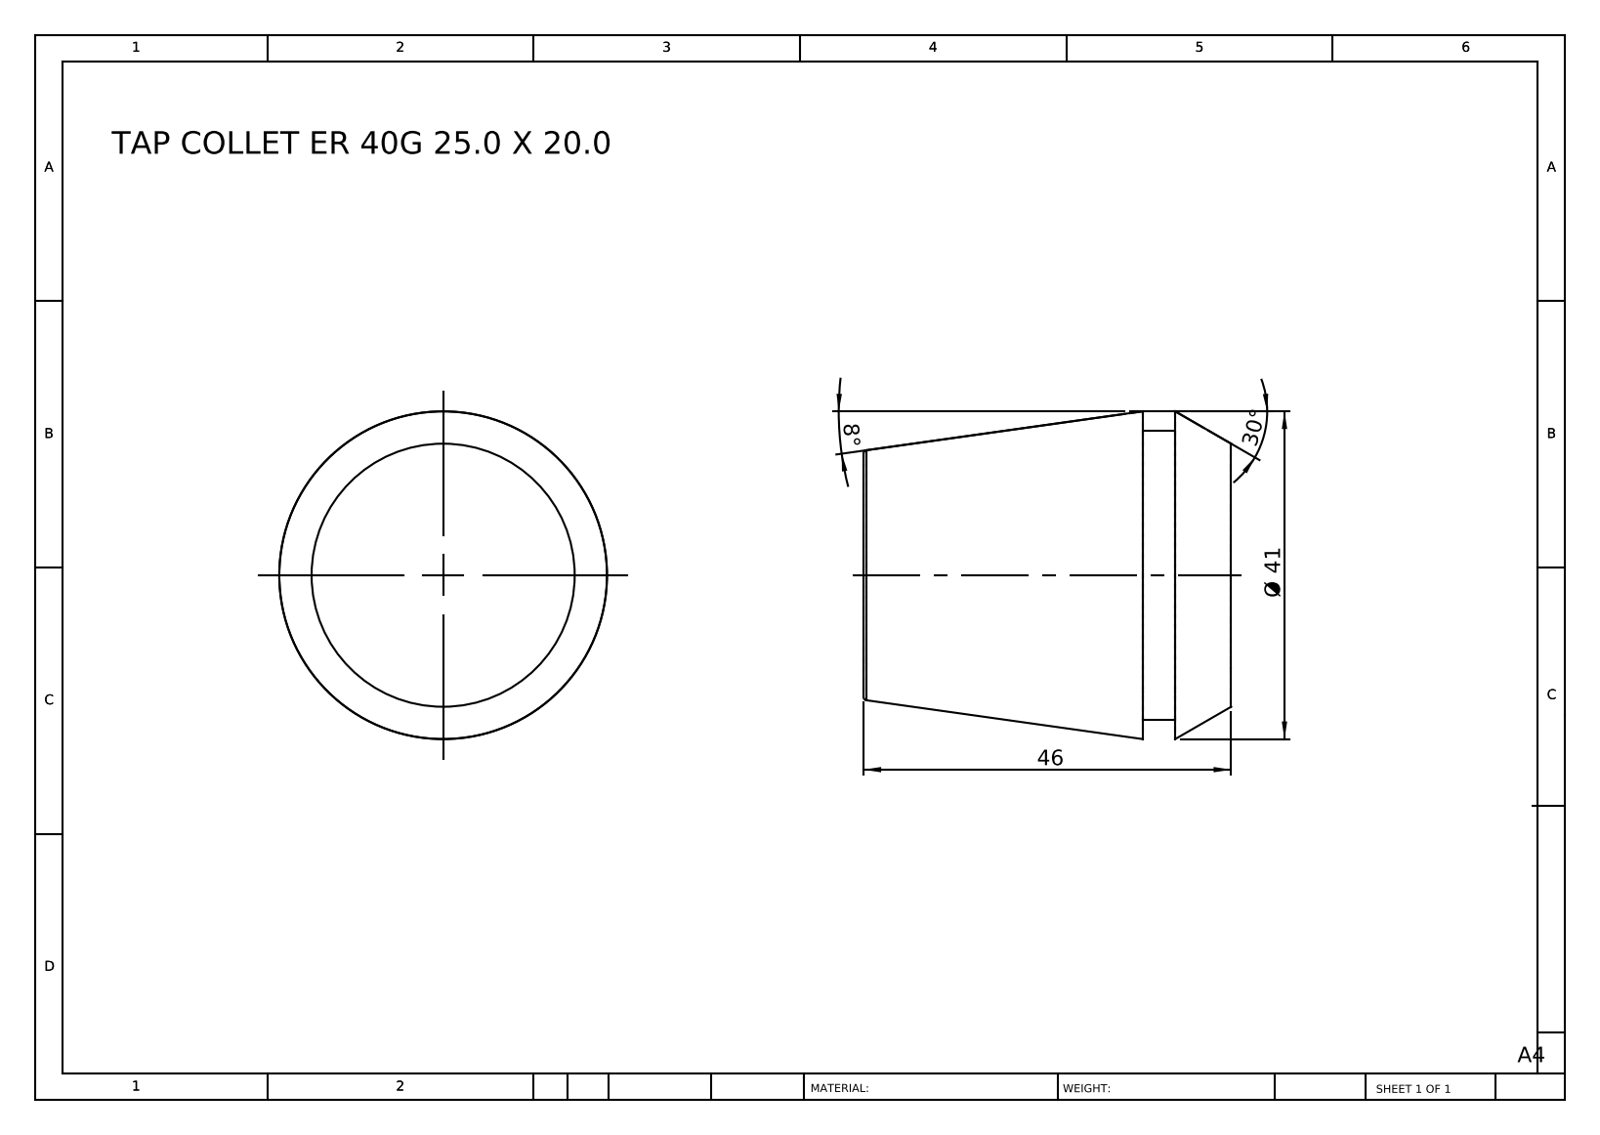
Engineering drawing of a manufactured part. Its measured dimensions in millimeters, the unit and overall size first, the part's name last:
Units: millimetres
Overall size (bounding box): 46 × 41 × 41
Round bosses / shafts (diameter × count): ⌀36.2 ×1
Main face-to-face distances: 46, 11.1, 34.9, 7, 4.1, 39
Volume: 47 690 mm³ · Surface area: 7 586 mm²
Bodies: 1 solid, 12 faces (4 planar, 2 cylindrical, 6 other)
Part name (STEP PRODUCT): TAP COLLET ER 40G 25.0 X 20.0
STEP written by: SolidWorks 2014 (CONFIG_CONTROL_DESIGN)
